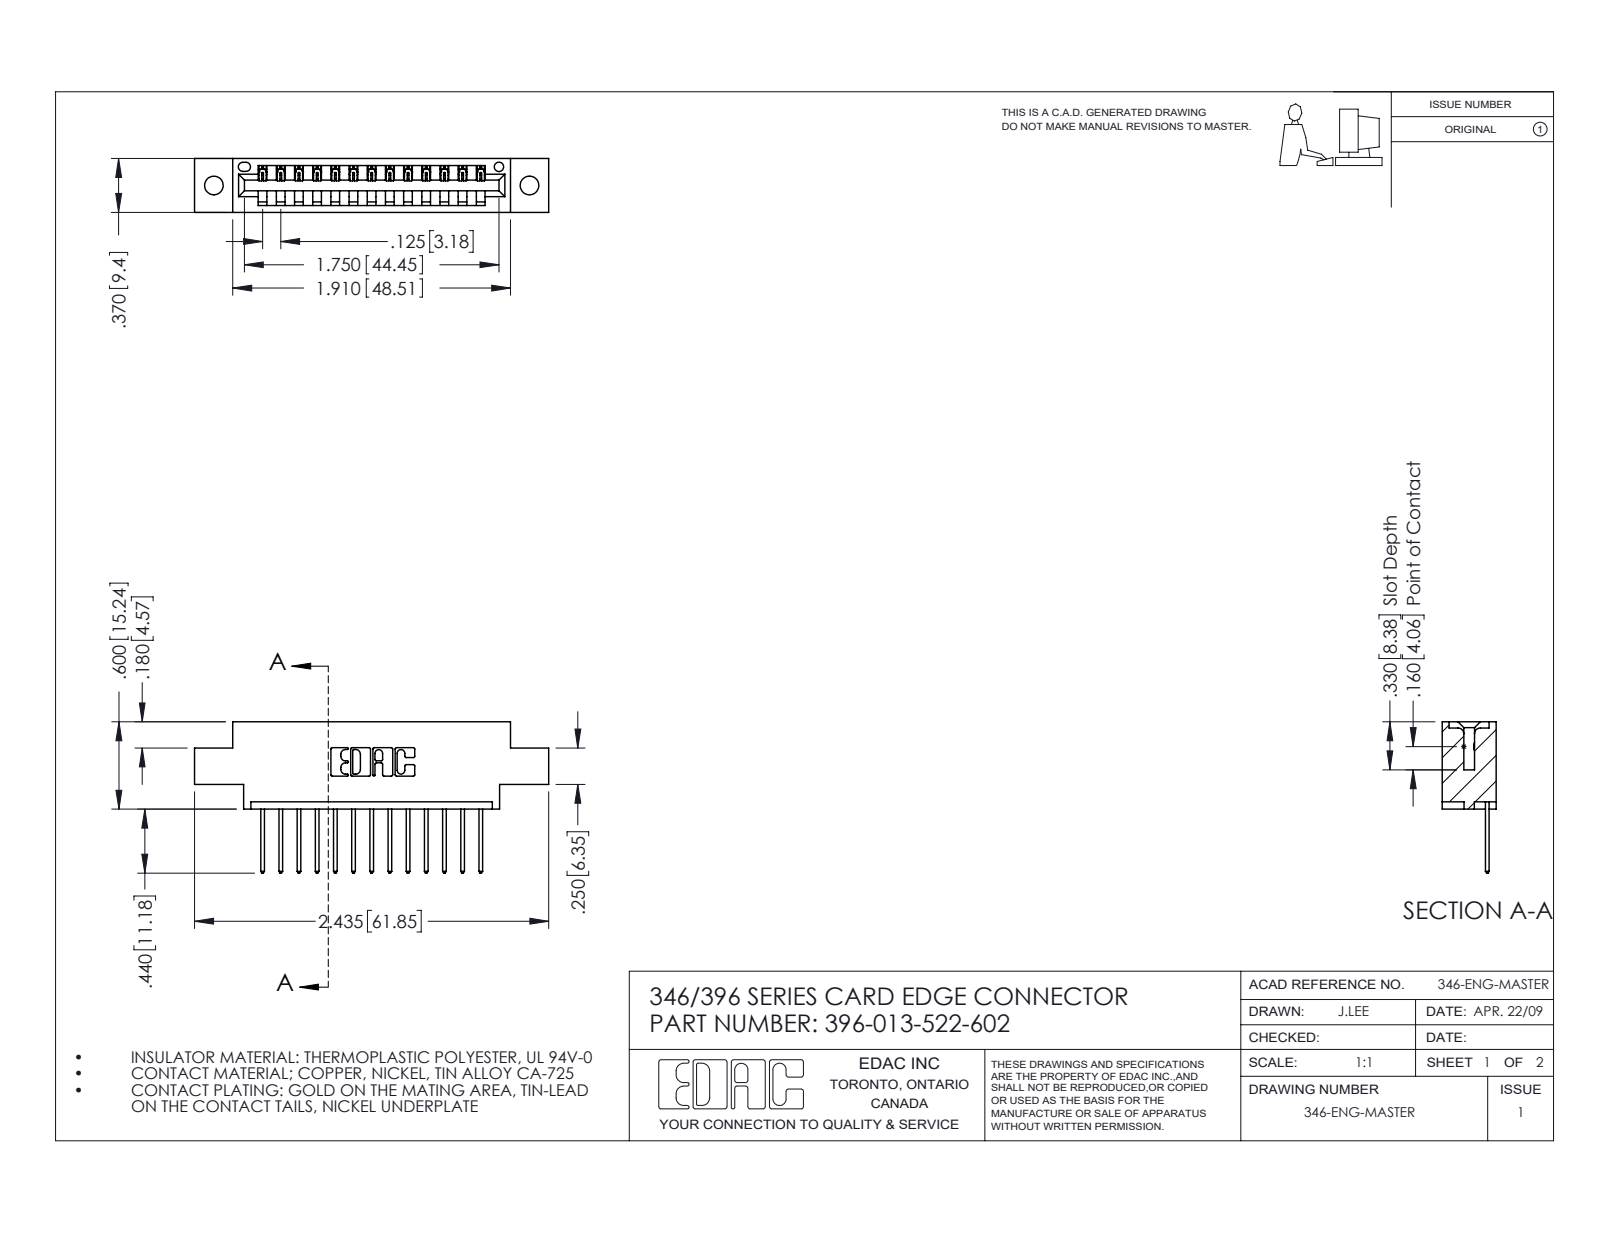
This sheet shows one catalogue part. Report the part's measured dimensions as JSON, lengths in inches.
{"part_name": "346 Part_0.170 Offset - 0.128 Dia; 396-013-522-602; 345-292-001_345-293-122", "step_written_by": "SolidWorks 2016 (CONFIG_CONTROL_DESIGN)", "units": "inches", "bodies": {"solids": 14, "faces": 880, "planar": 600, "cylindrical": 280, "other": 0}, "overall_size": [2.435, 1.04, 0.37], "volume_in3": 0.338, "surface_area_in2": 10.13, "round_holes": [[0.128, 2], [0.064, 1]], "partial_cylinders_radius": [[0.006, 26], [0.01, 26], [0.01, 22], [0.007, 6], [0.031, 6], [0.026, 3], [0.031, 2], [0.04, 2]], "face_to_face_distances": [0.25, 0.37, 0.048, 0.322, 0.072, 0.298, 0.025, 0.148, 0.222, 0.1], "hole_center_spacings": [0.246, 1.964, 2.17]}
